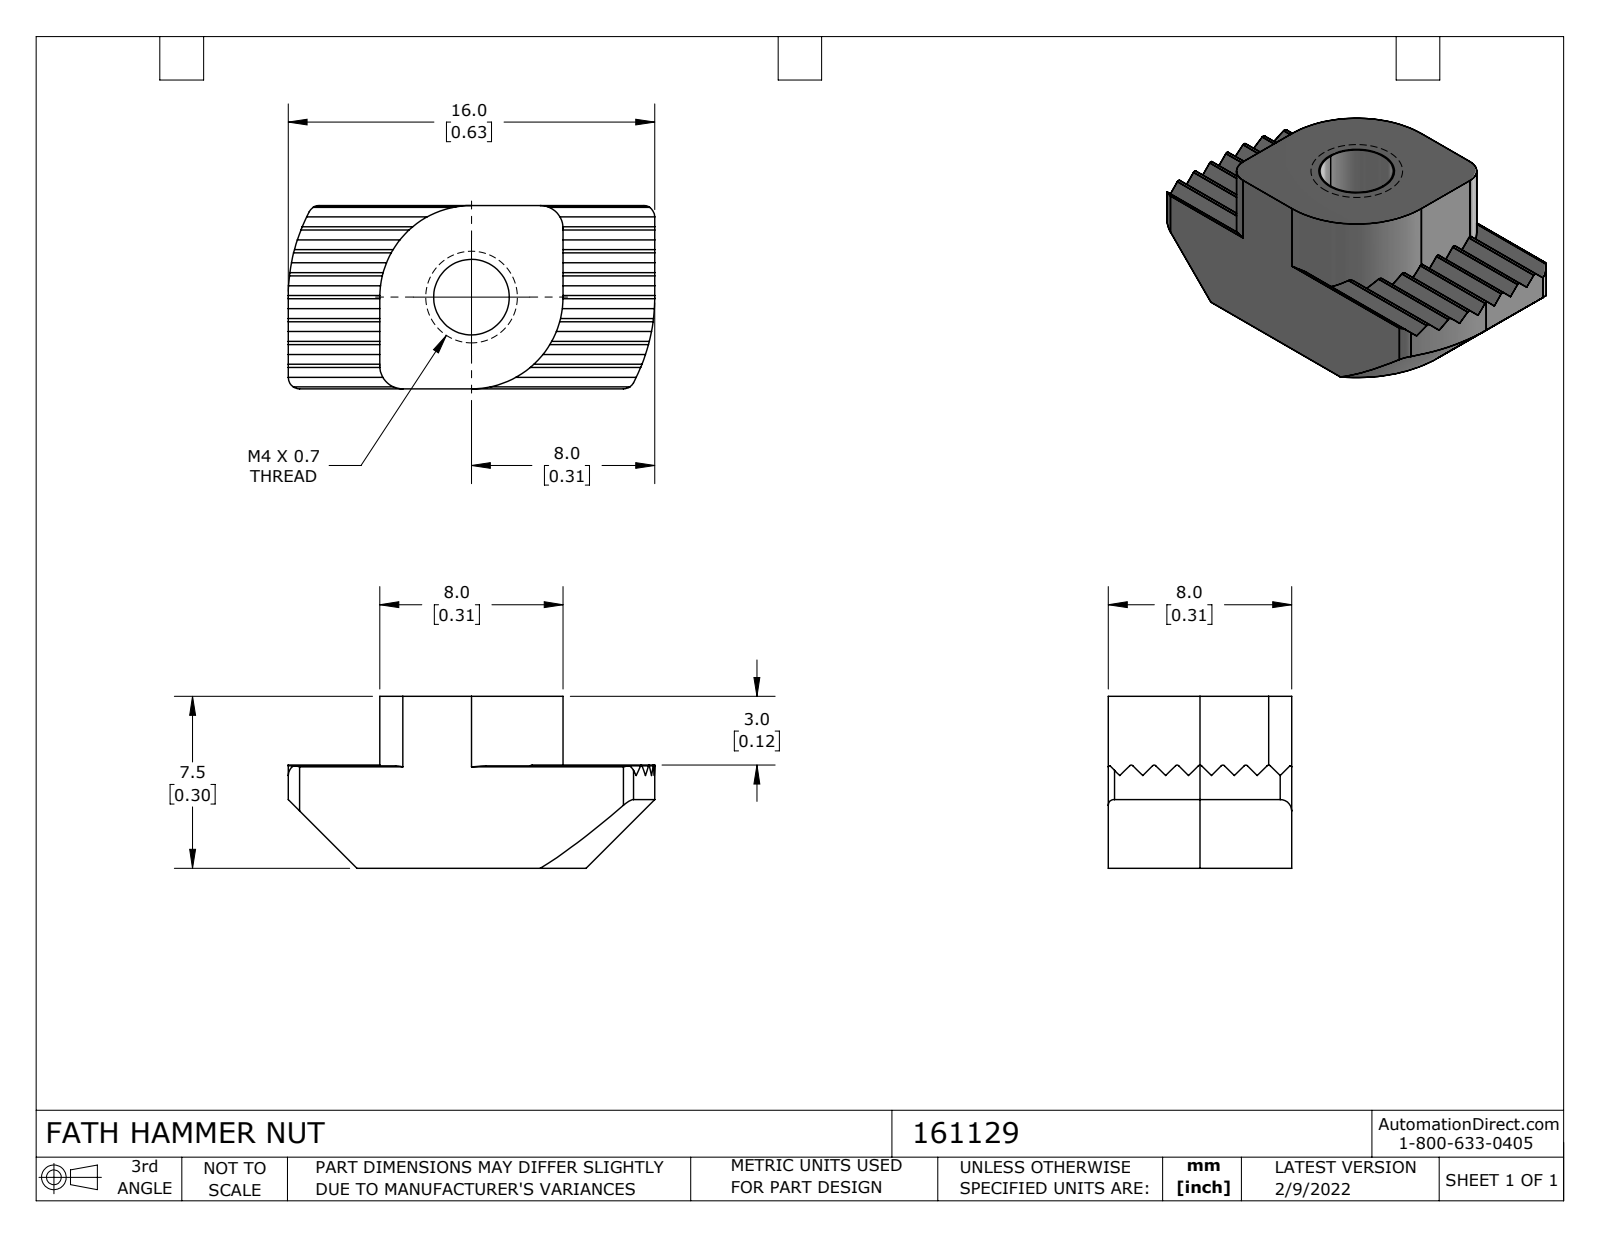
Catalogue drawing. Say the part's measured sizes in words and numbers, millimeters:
The part is named "161129". Its 3-D file was written by "SolidWorks 2021 (CONFIG_CONTROL_DESIGN)". It is 2 solids with 152 faces: 84 planar, 64 cylindrical and 4 other. Overall it measures 16 by 8 by 7.5 millimeters. Its volume is 1 164 cubic millimeters and its surface area 1 153 square millimeters. Round holes: 1 of diameter 3.2, 1 of diameter 3.3. Partial cylindrical surfaces (rounded edges, fillets, slot ends): 7 of radius 0.1, 4 of radius 0.5, 2 of radius 1, 1 of radius 4, 1 of radius 8. The main face-to-face distances are 8, 0.71, 2.12, 7.5, 1.41, 2.83, 4.24, 3.53, 1.42, 0.7.
